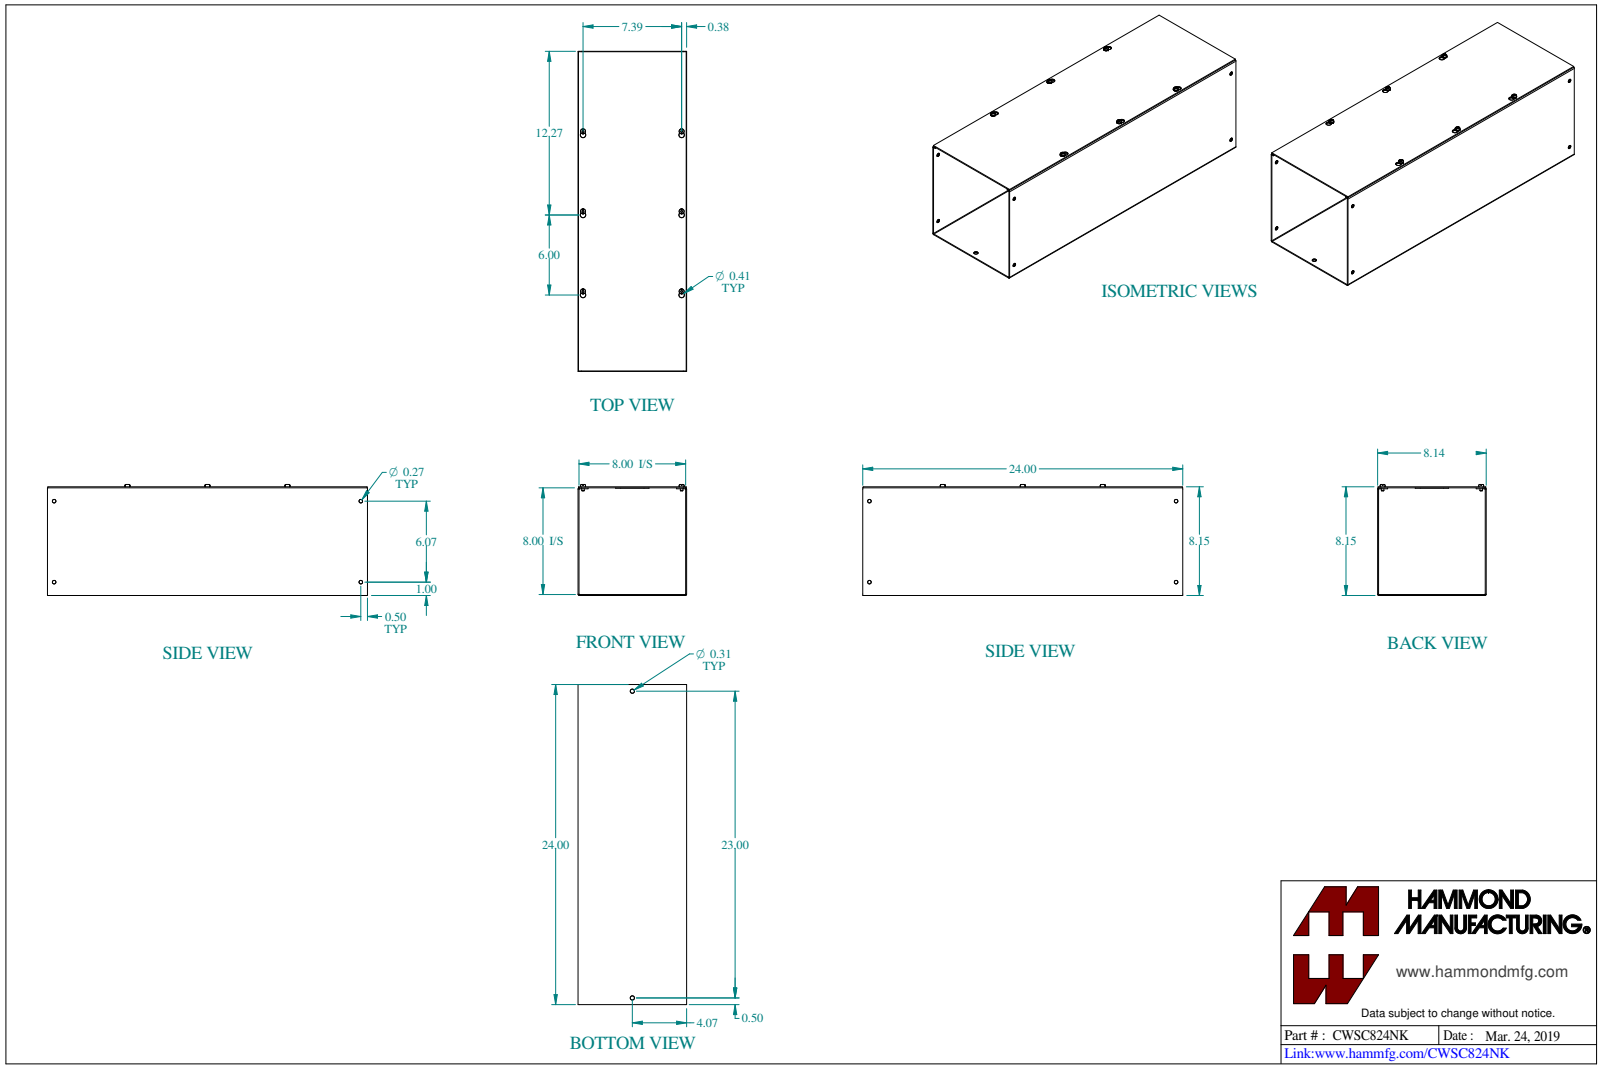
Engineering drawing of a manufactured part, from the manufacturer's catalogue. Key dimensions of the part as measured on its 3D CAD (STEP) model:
Part name (STEP PRODUCT): CWSC824NK
STEP written by: SolidWorks 2023 (CONFIG_CONTROL_DESIGN)
Units: inches
Bodies: 8 solids, 242 faces (118 planar, 88 cylindrical, 36 other)
Overall size (bounding box): 24 × 8.325 × 8.144
Volume: 58.8 in³ · Surface area: 1 615 in²
Round holes (diameter × count): ⌀0.177 ×6, ⌀0.266 ×4, ⌀0.313 ×2
Round bosses / shafts (diameter × count): ⌀0.375 ×6, ⌀0.19 ×6
Partial cylindrical surfaces — rounded edges, fillets, slot ends (radius × count): R0.125 ×6, R0.203 ×6, R0.036 ×4, R0.108 ×4
Main face-to-face distances: 0.072, 8.072, 8, 0.078, 8.15, 8.078, 8.144, 7.928, 0.15, 0.031
Hole centre spacings: 6, 6.627, 9.522, 12.08, 17.886, 7.394, 23, 6.072
